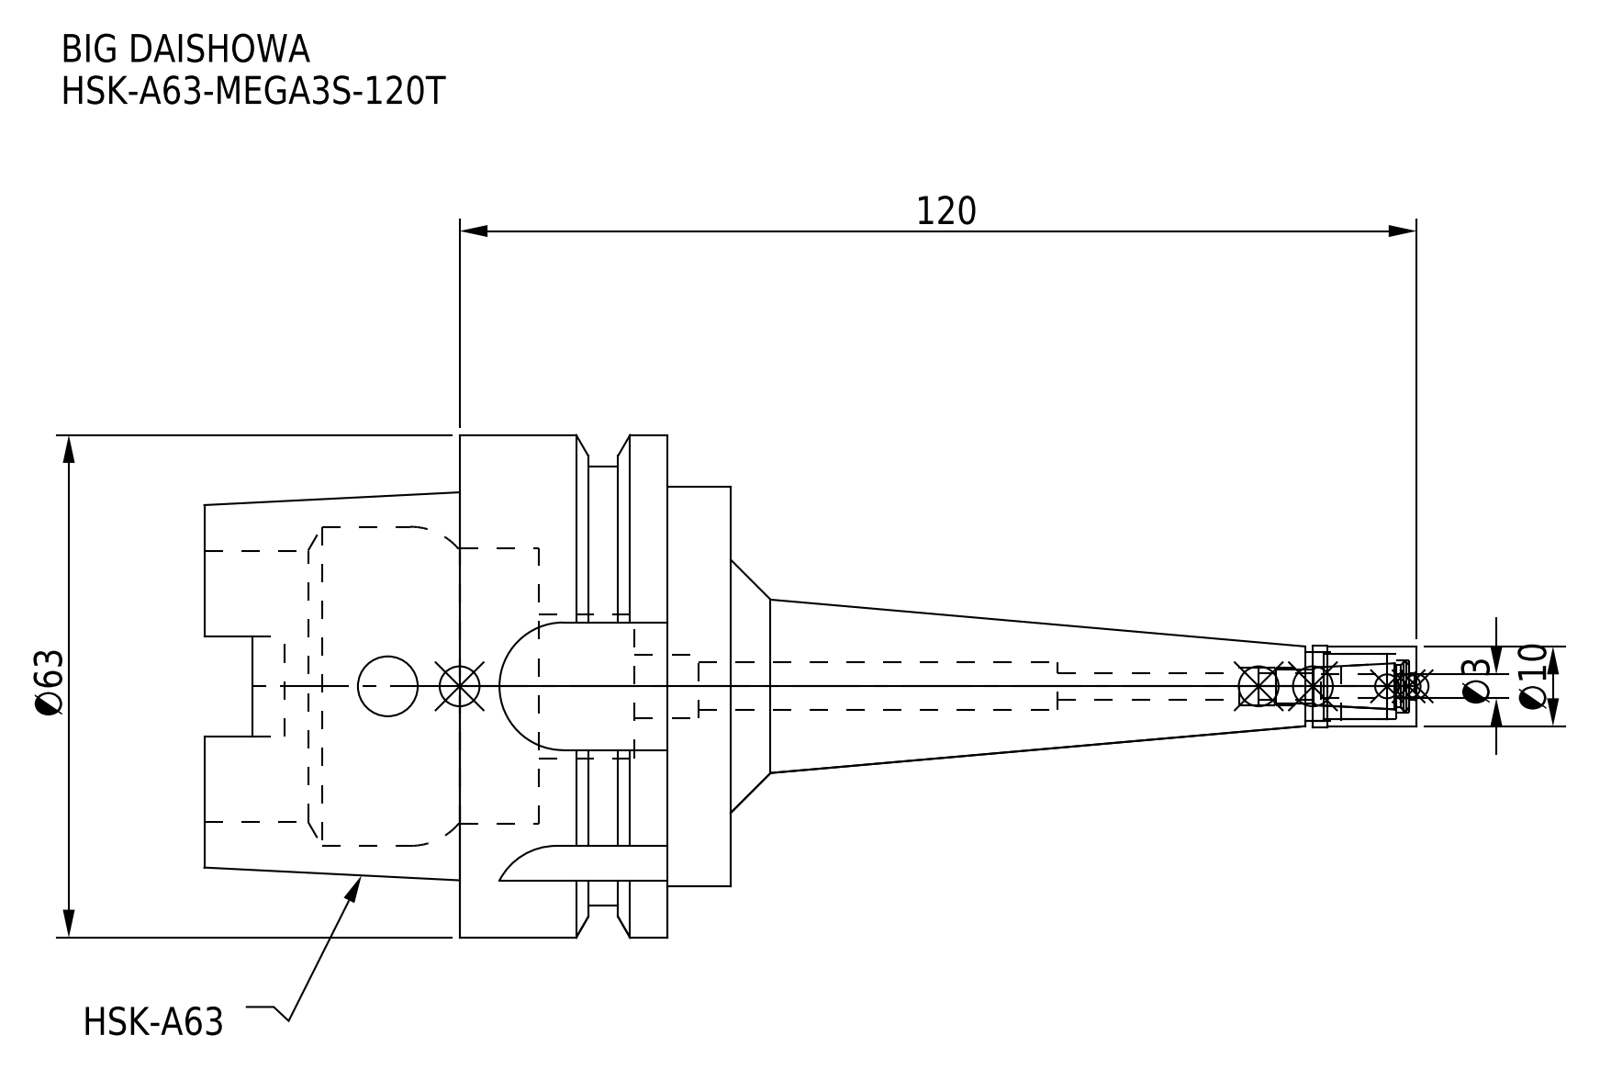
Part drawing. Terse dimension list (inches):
name: HSK-A63-MEGA3S-120T; DXF_TEMP_ASSY_ASM_4_ASM.stp; HA63MS03120T-030_ASM.stp; HSK-A63-MEGA3S-120T_1.stp (+3 more)
written by: SolidWorks 2019 (CONFIG_CONTROL_DESIGN)
unit: in
bodies: 2 solids, 125 faces (48 planar, 55 cylindrical, 22 other)
size: 5.984 × 2.48 × 2.48
volume: 6.893 in³; area: 45.74 in²
holes: 1× ⌀0.13, 1× ⌀0.134, 1× ⌀0.185, 1× ⌀0.236, 1× ⌀0.26, 1× ⌀0.295, 1× ⌀0.315, 1× ⌀0.323, 1× ⌀0.343, 1× ⌀0.709, 1× ⌀1.339, 1× ⌀1.358
bosses: 1× ⌀2.48, 1× ⌀2.165, 1× ⌀1.969, 1× ⌀0.406, 1× ⌀0.394
rounds: 4× R0.113, 4× R0.315
face distances: 1.339, 1.024, 0.315, 0.947, 0.632, 0.392, 1.26, 2.598, 2.283, 1.652
